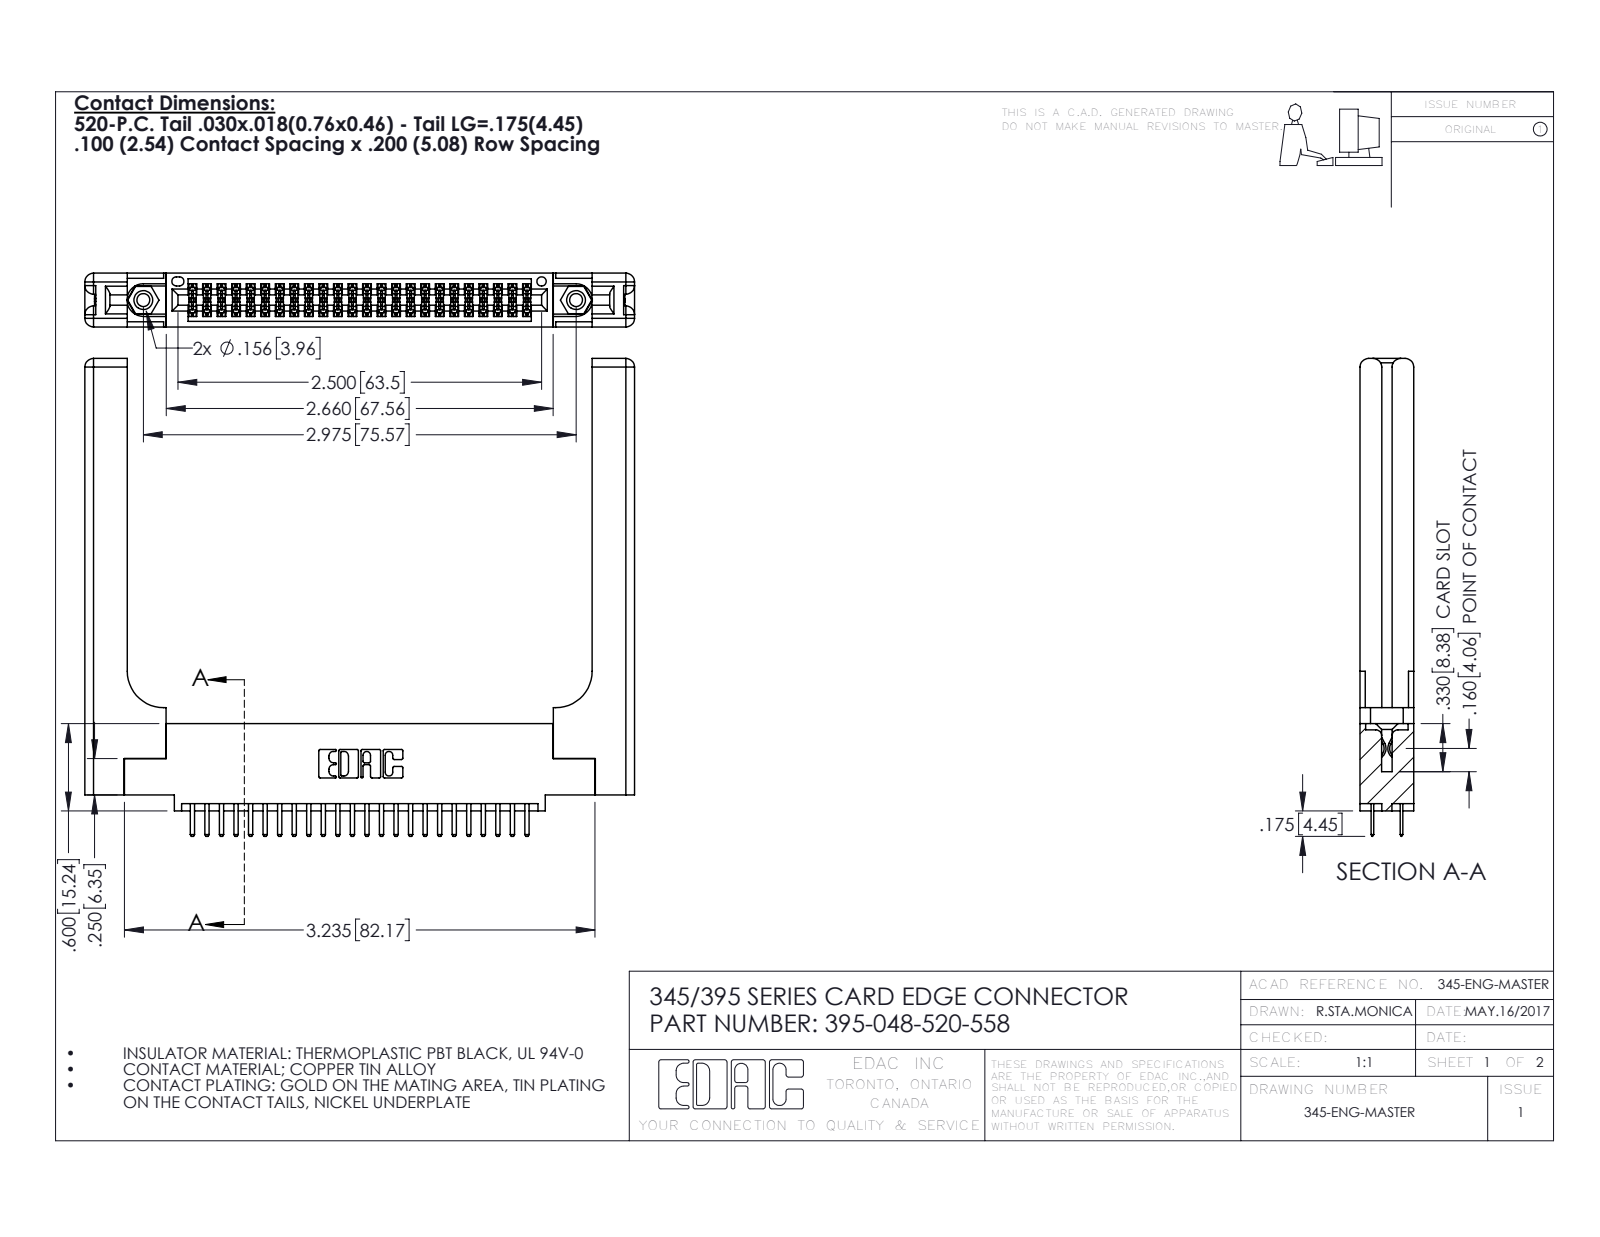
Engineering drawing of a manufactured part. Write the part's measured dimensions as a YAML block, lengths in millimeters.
part_name: "345-220-058_345-220-058; 345 Part_0.110 Offset - 0.156 Dia-TH; 345-250-001_345-250-001-102; 395-048-520-558 (+1 more)"
step_written_by: "SolidWorks 2016 (CONFIG_CONTROL_DESIGN)"
units: millimeters
bodies: {solids: 53, faces: 2978, planar: 1912, cylindrical: 1006, other: 60}
overall_size: [96, 83.4, 9.4]
volume: 17530
surface_area: 18150
round_holes:
  - {diameter: 2.3, count: 2}
  - {diameter: 3.2, count: 2}
  - {diameter: 4, count: 2}
  - {diameter: 1.6, count: 1}
round_bosses_or_shafts:
  - {diameter: 3.9, count: 2}
partial_cylinders:
  - {radius: 0.2, count: 72}
  - {radius: 0.3, count: 52}
  - {radius: 0.3, count: 22}
  - {radius: 1.5, count: 16}
  - {radius: 0.2, count: 6}
  - {radius: 0.8, count: 6}
  - {radius: 0.7, count: 3}
  - {radius: 0.4, count: 2}
face_to_face_distances: [9.4, 1.8, 7.6, 5.1, 3.8, 3.8, 2.5, 6.9, 0.6, 5.6]
hole_center_spacings: [6.9, 69.6, 75.6]
